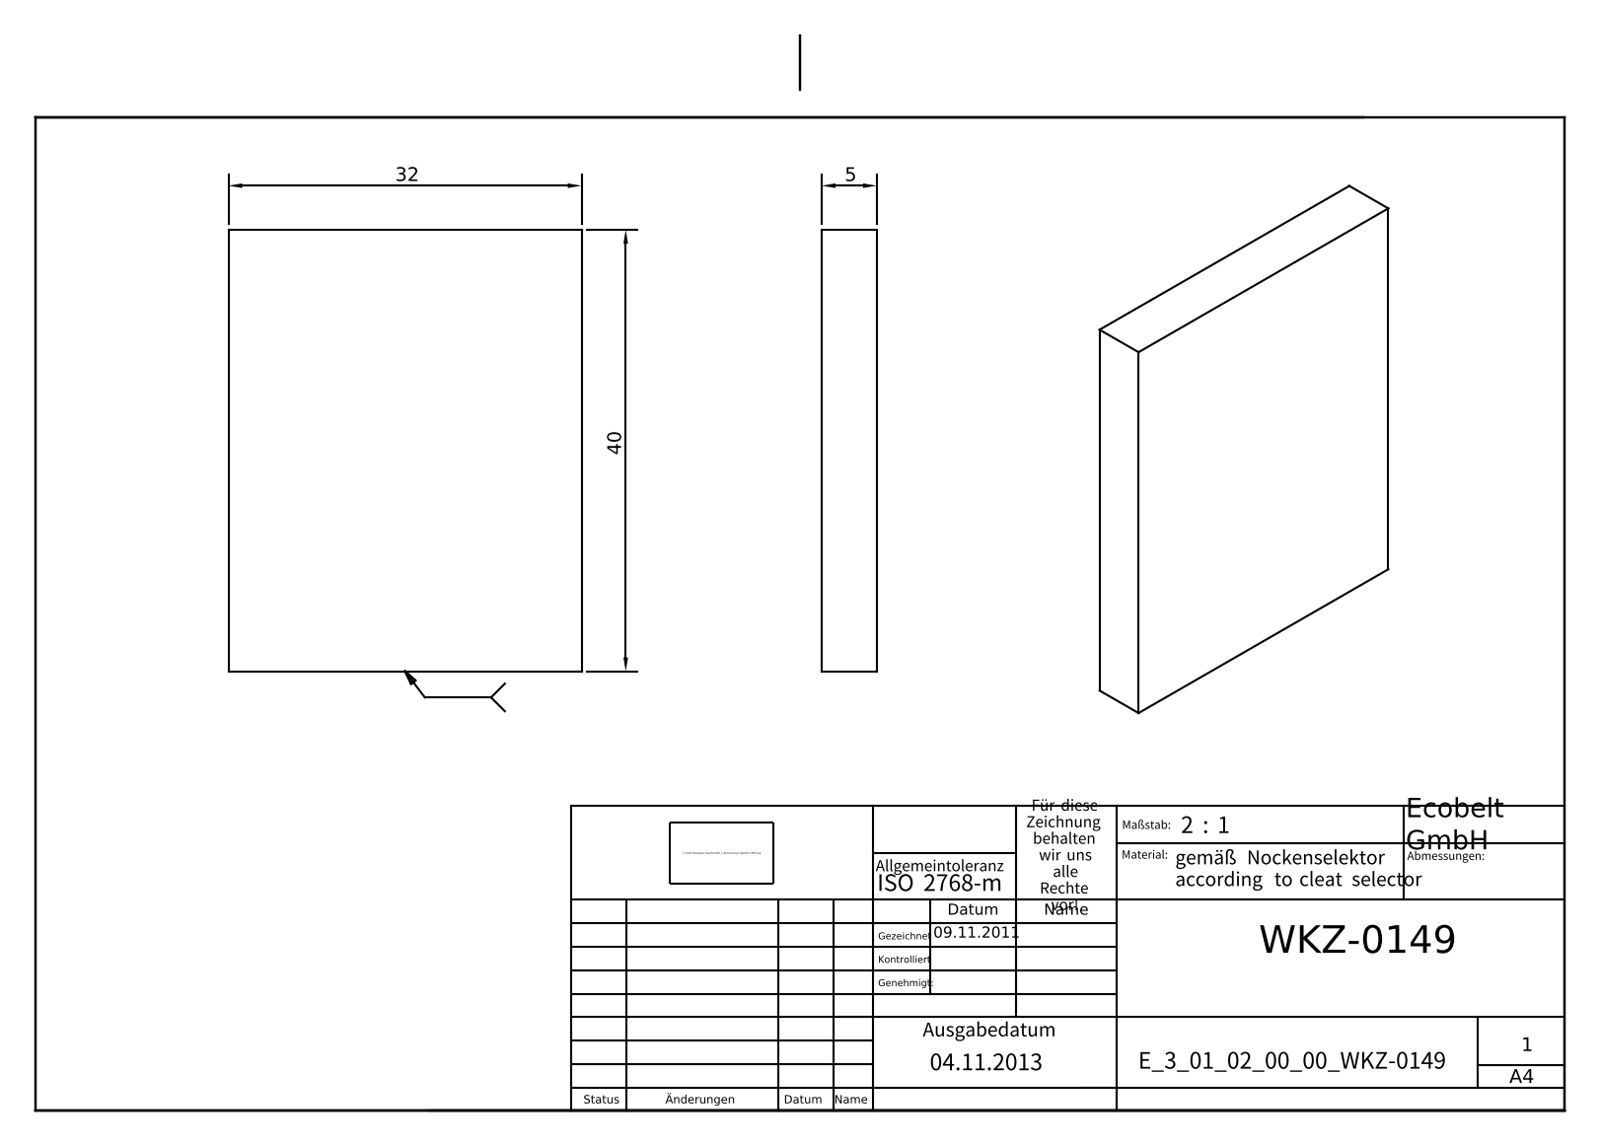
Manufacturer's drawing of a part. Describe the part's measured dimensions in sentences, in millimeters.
The part is named "E_3_01_02_00_00_WKZ-0149". Its 3-D file was written by "Autodesk Inventor 2021 (AUTOMOTIVE_DESIGN)". It is 1 solid with 6 faces: 6 planar, 0 cylindrical and 0 other. Overall it measures 40 by 32 by 5 millimeters. Its volume is 6 400 cubic millimeters and its surface area 3 280 square millimeters. The main face-to-face distances are 5, 32, 40.
